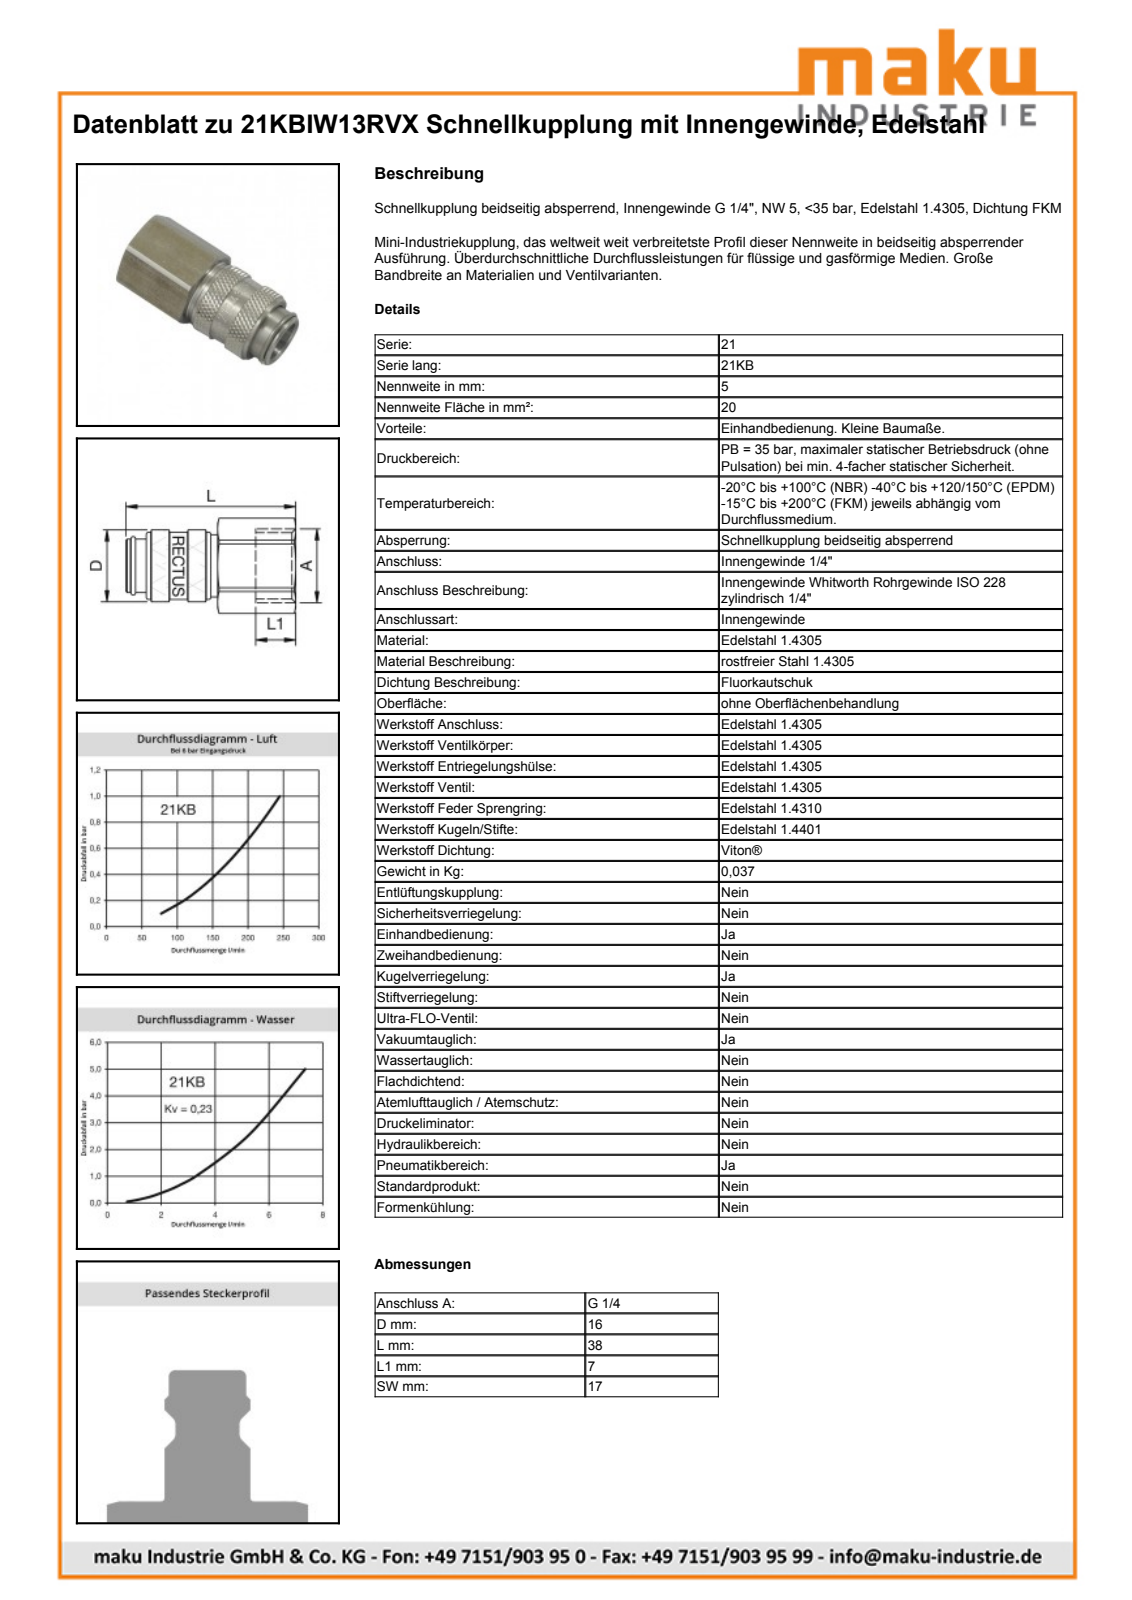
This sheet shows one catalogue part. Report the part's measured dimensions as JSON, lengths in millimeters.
{"part_name": "D106121", "step_written_by": "Autodesk Inventor 2011 (AUTOMOTIVE_DESIGN)", "units": "millimeters", "bodies": {"solids": 2, "faces": 392, "planar": 130, "cylindrical": 59, "other": 203}, "overall_size": [38.15, 19.15, 17.03], "volume_mm3": 6691, "surface_area_mm2": 4105, "round_holes": [[7.5, 1], [11.45, 1], [12.15, 1], [14, 1]], "round_bosses_or_shafts": [[16.15, 1], [15.1, 1], [12, 1], [11.15, 1]], "partial_cylinders_radius": [[5.39, 1], [7.45, 1], [9.57, 1]], "face_to_face_distances": [17, 38.15, 20.6, 17.55, 9, 29.15, 8.55, 29.14, 8.54, 9.01]}
